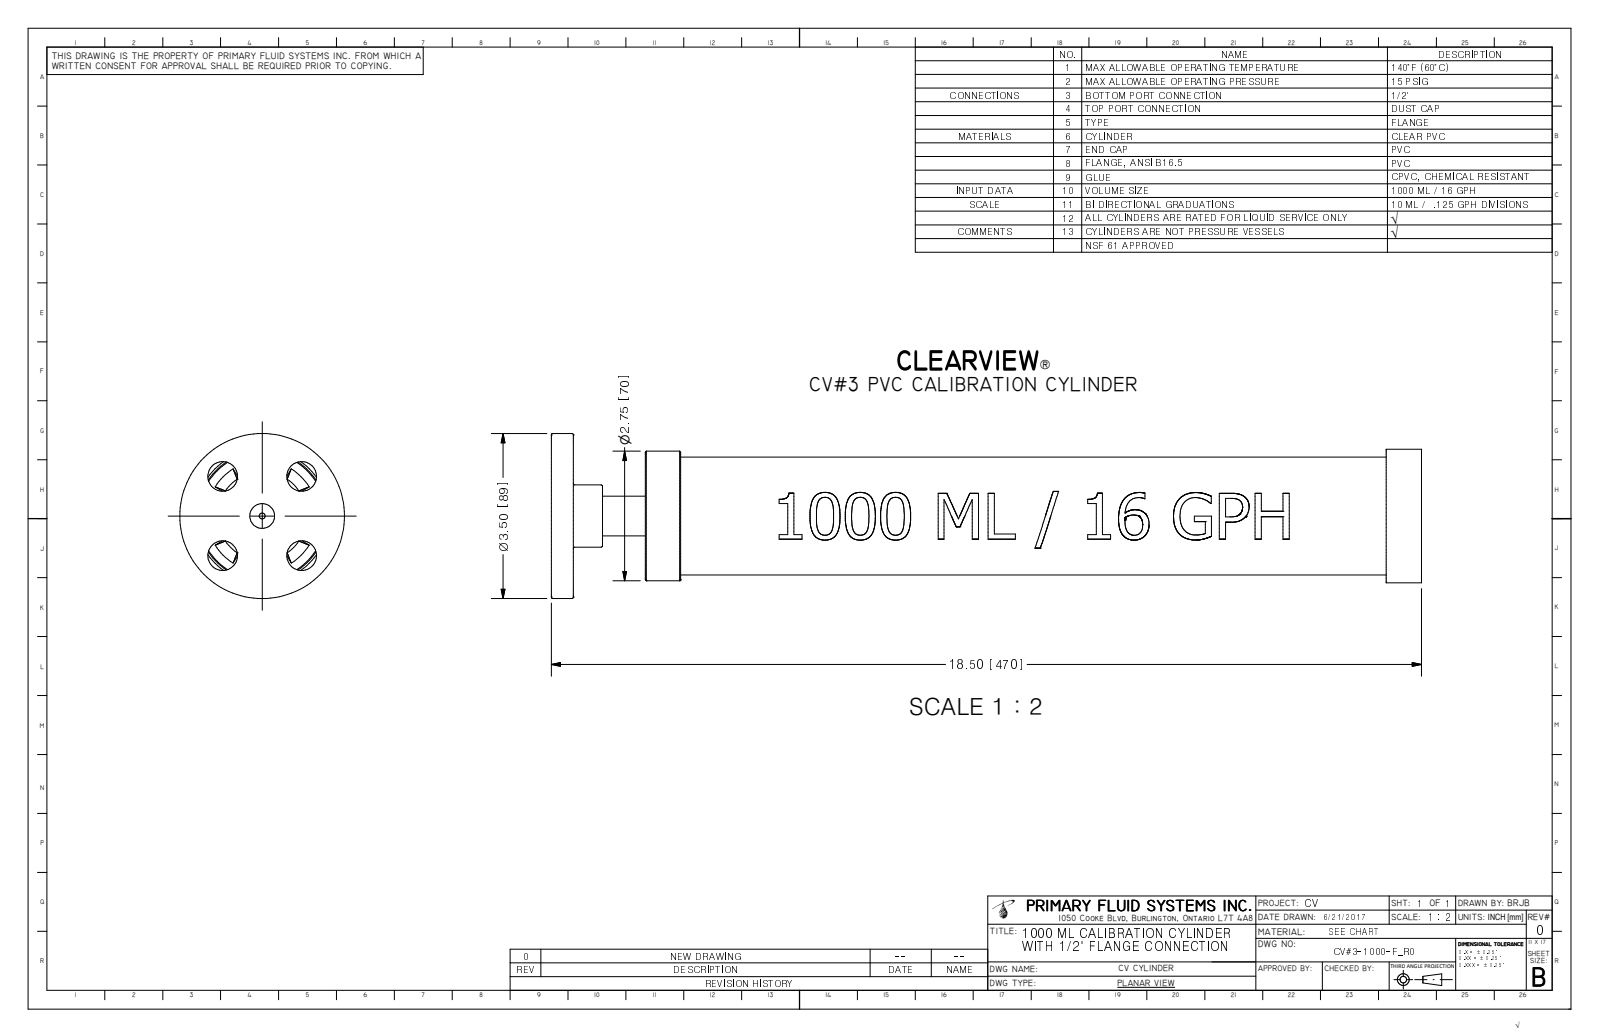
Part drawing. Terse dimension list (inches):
name: PV#3-1000-F_R0
written by: Autodesk Inventor 2009 (AUTOMOTIVE_DESIGN)
unit: in
bodies: 2 solids, 260 faces (92 planar, 31 cylindrical, 137 other)
size: 18.5 × 3.5 × 3.5
volume: 19.89 in³; area: 327.5 in²
holes: 4× ⌀0.63, 1× ⌀0.526, 1× ⌀0.719, 1× ⌀2.38, 1× ⌀2.52
bosses: 1× ⌀3.5, 1× ⌀2.832, 1× ⌀2.75, 1× ⌀2.5, 1× ⌀2.36, 1× ⌀1.32
rounds: 1× R1.249
face distances: 0.47, 0.75, 18.5, 18.03, 17.75, 17.28, 15.75, 2, 1.53, 16.5
hole spacings: 1.188, 1.68, 2.375
